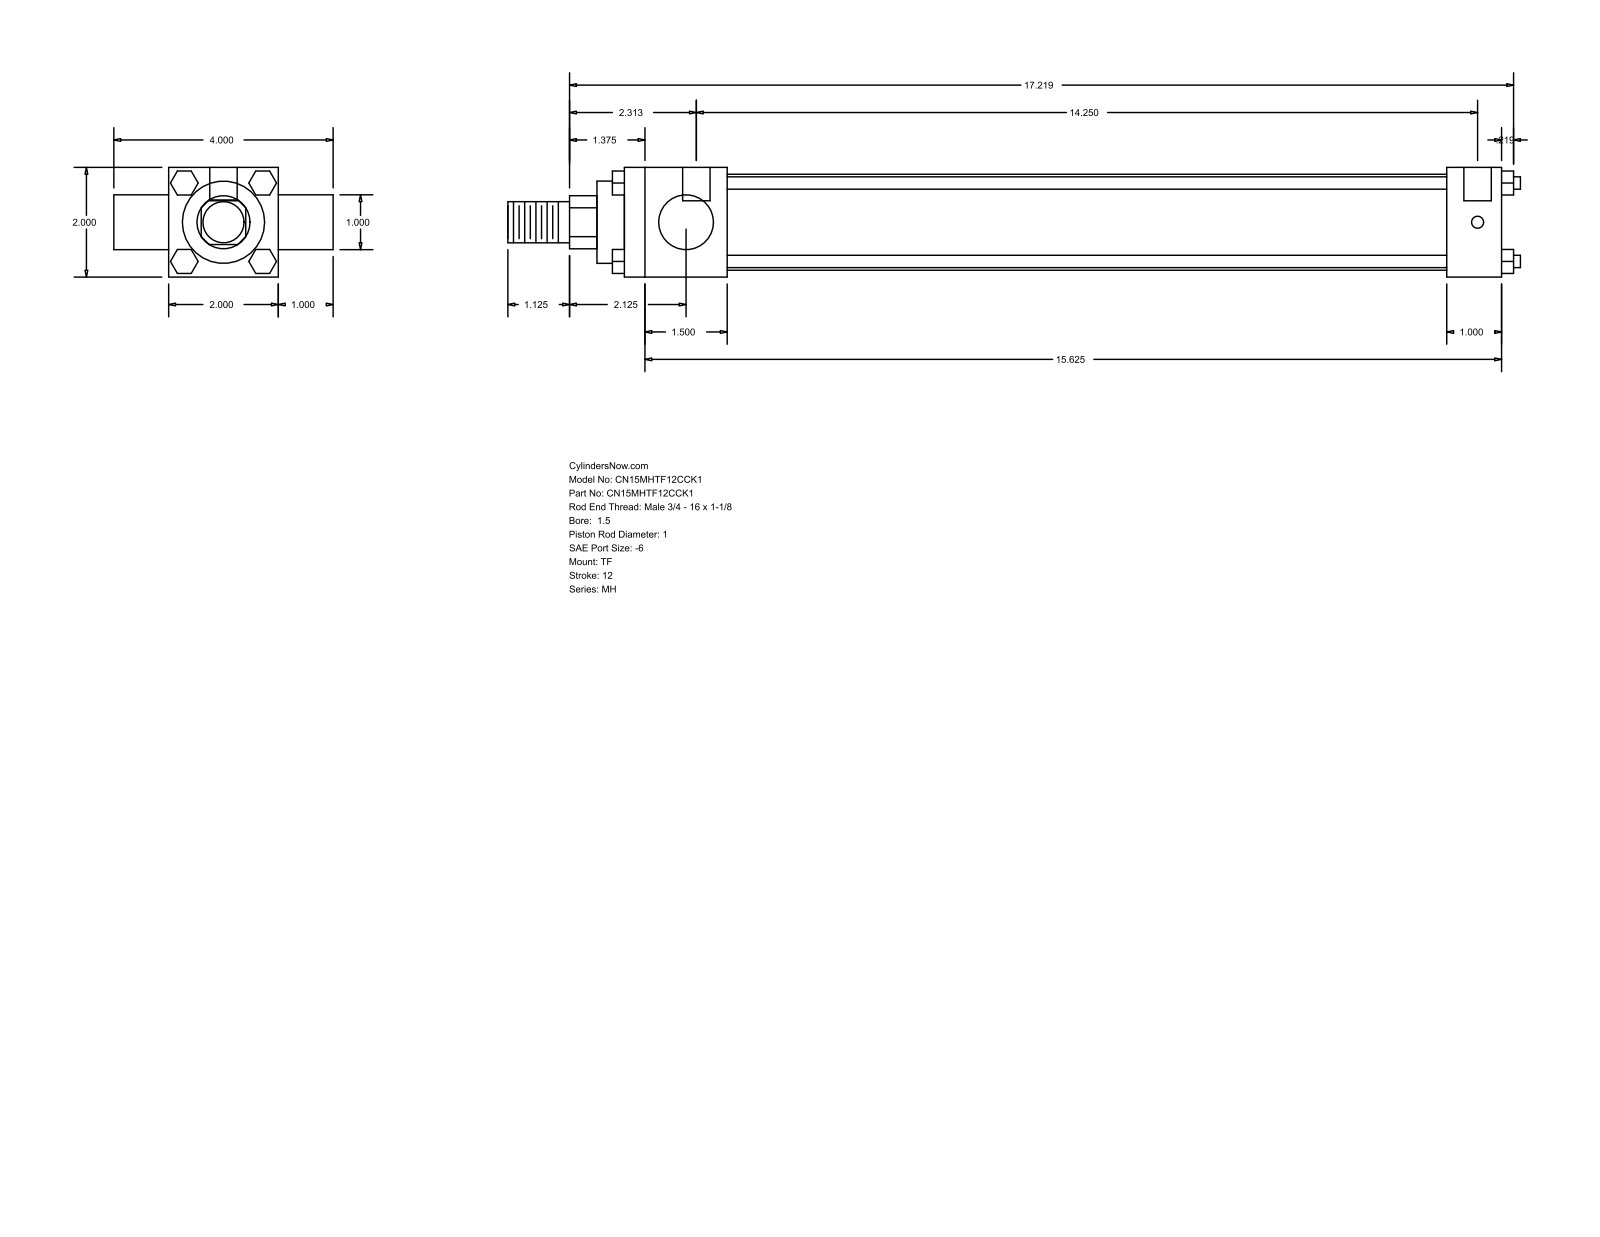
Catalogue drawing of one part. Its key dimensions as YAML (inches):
part_name: "MH_TF__0150_1"
step_written_by: "GSSL Pune (CONFIG_CONTROL_DESIGN)"
units: inches
bodies: {solids: 0, faces: 120, planar: 92, cylindrical: 28, other: 0}
overall_size: [18.469, 4, 2]
round_holes:
  - {diameter: 0.219, count: 3}
  - {diameter: 0.5, count: 2}
round_bosses_or_shafts:
  - {diameter: 0.225, count: 4}
  - {diameter: 1, count: 2}
  - {diameter: 1.75, count: 1}
  - {diameter: 1.5, count: 1}
  - {diameter: 0.75, count: 1}
partial_cylinders:
  - {radius: 0.484, count: 1}
face_to_face_distances: [2, 1, 16, 3, 1.875, 14.125, 15, 13.125, 4, 0.5]
hole_center_spacings: [0.125, 14.25, 14.375]
